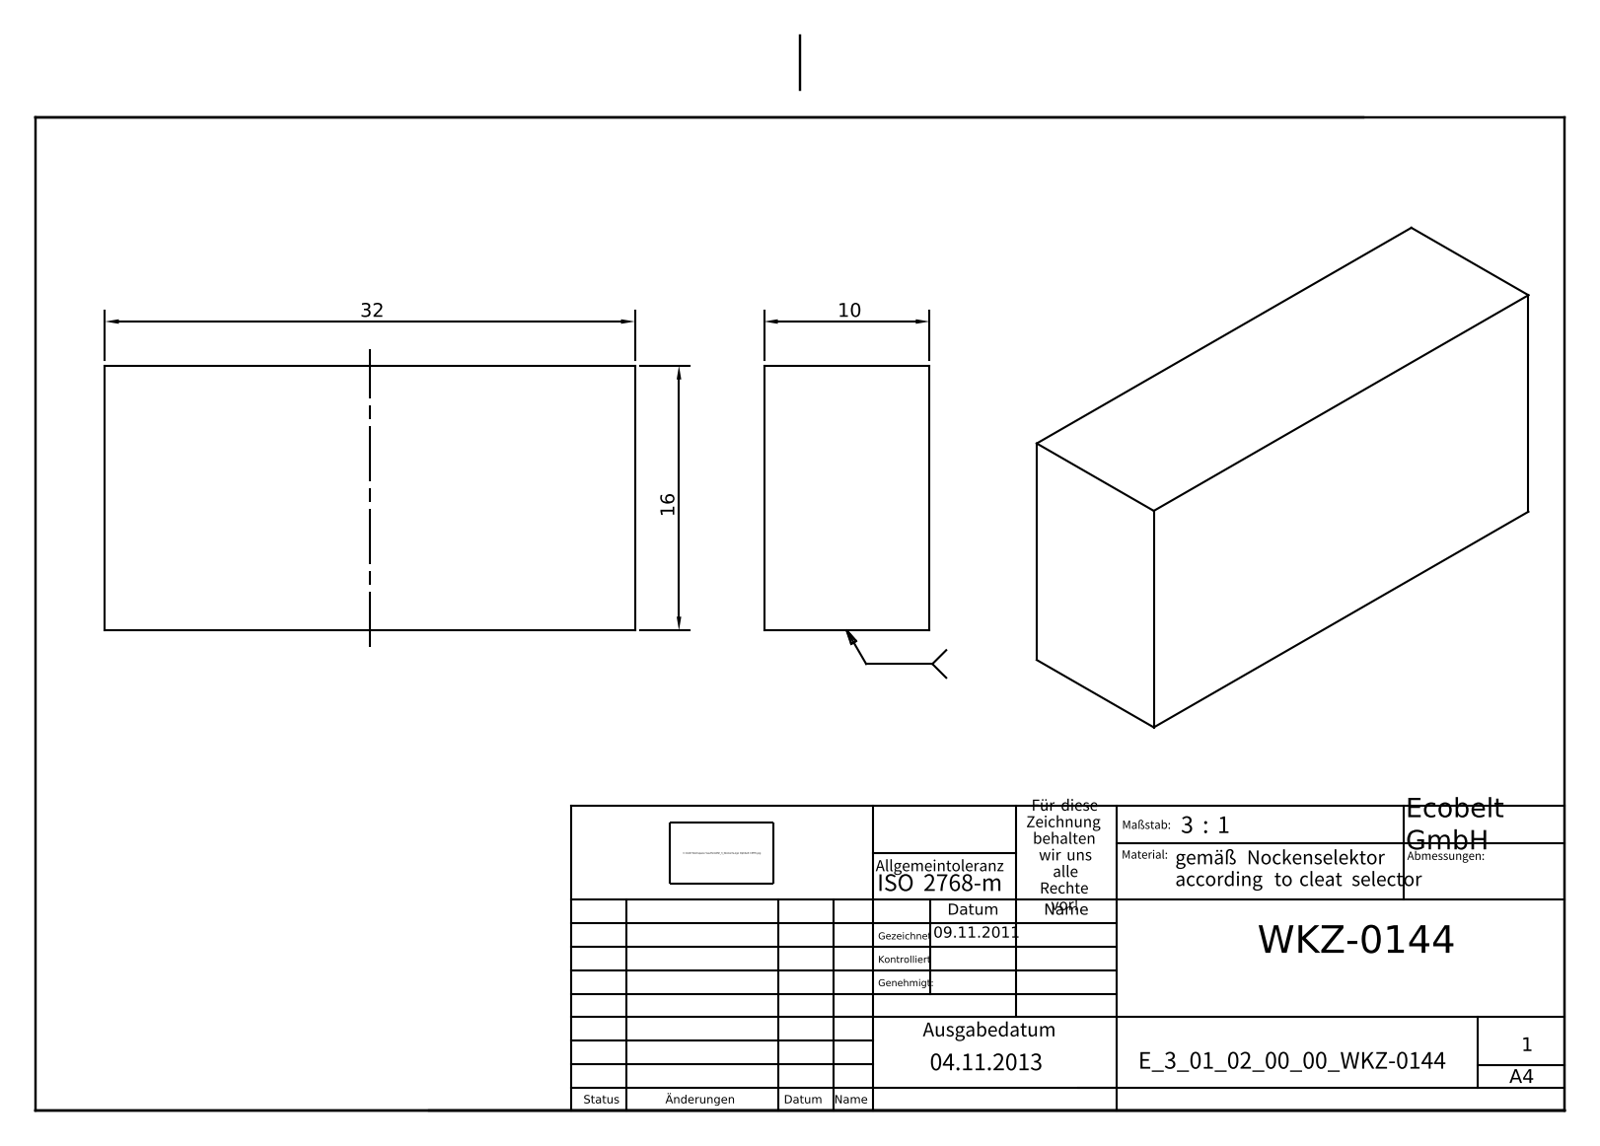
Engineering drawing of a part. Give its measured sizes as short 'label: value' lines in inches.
name: E_3_01_02_00_00_WKZ-0144
written by: Autodesk Inventor 2021 (AUTOMOTIVE_DESIGN)
unit: in
bodies: 1 solid, 6 faces (6 planar, 0 cylindrical, 0 other)
size: 1.26 × 0.63 × 0.394
volume: 0.312 in³; area: 3.075 in²
face distances: 0.394, 0.63, 1.26
